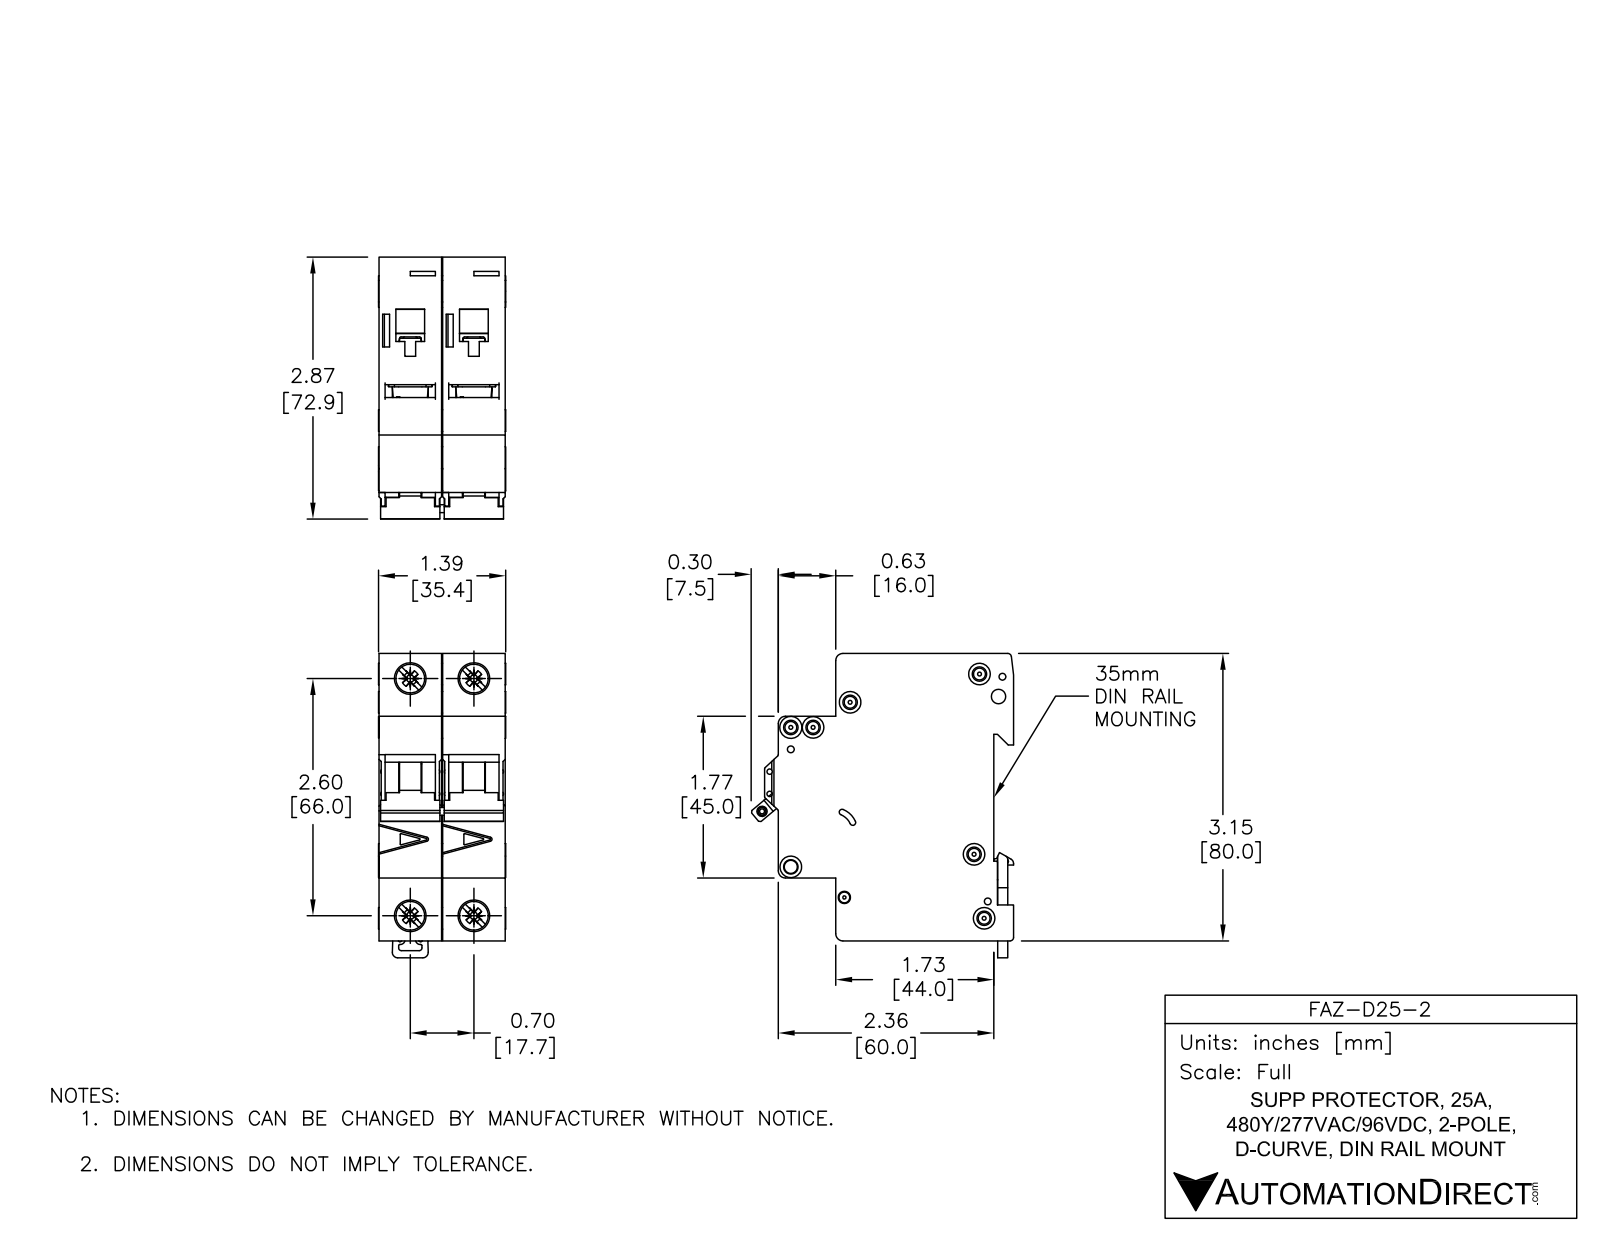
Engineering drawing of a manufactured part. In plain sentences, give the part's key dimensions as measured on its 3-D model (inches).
The part is named "FAZ-D25-2". Its 3-D file was written by "SolidWorks 2014 (AUTOMOTIVE_DESIGN)". It is 8 solids with 1104 faces: 466 planar, 396 cylindrical and 242 other. Overall it measures 3.338 by 2.876 by 1.394 inches. Its volume is 9.142 cubic inches and its surface area 60.14 square inches. Round holes: 6 of diameter 0.142, 3 of diameter 0.075, 2 of diameter 0.043, 2 of diameter 0.059, 2 of diameter 0.157, 2 of diameter 0.281, 2 of diameter 0.323, 1 of diameter 0.085, 1 of diameter 0.087, 1 of diameter 0.1, 1 of diameter 0.13, 1 of diameter 0.134. Round bosses or shafts: 4 of diameter 0.236, 2 of diameter 0.323, 2 of diameter 0.098. Partial cylindrical surfaces (rounded edges, fillets, slot ends): 49 of radius 0.01, 19 of radius 0.02, 10 of radius 0.079, 8 of radius 0.008, 8 of radius 0.039, 2 of radius 0.031, 2 of radius 0.071, 2 of radius 0.118. The main face-to-face distances are 0.697, 0.689, 1.386, 3.129, 0.217, 1.949, 1.732, 2.579, 2.362, 0.63. The hole center spacings are 0.244, 0.537, 0.697, 2.598, 2.69, 0.189, 0.204, 0.221.
